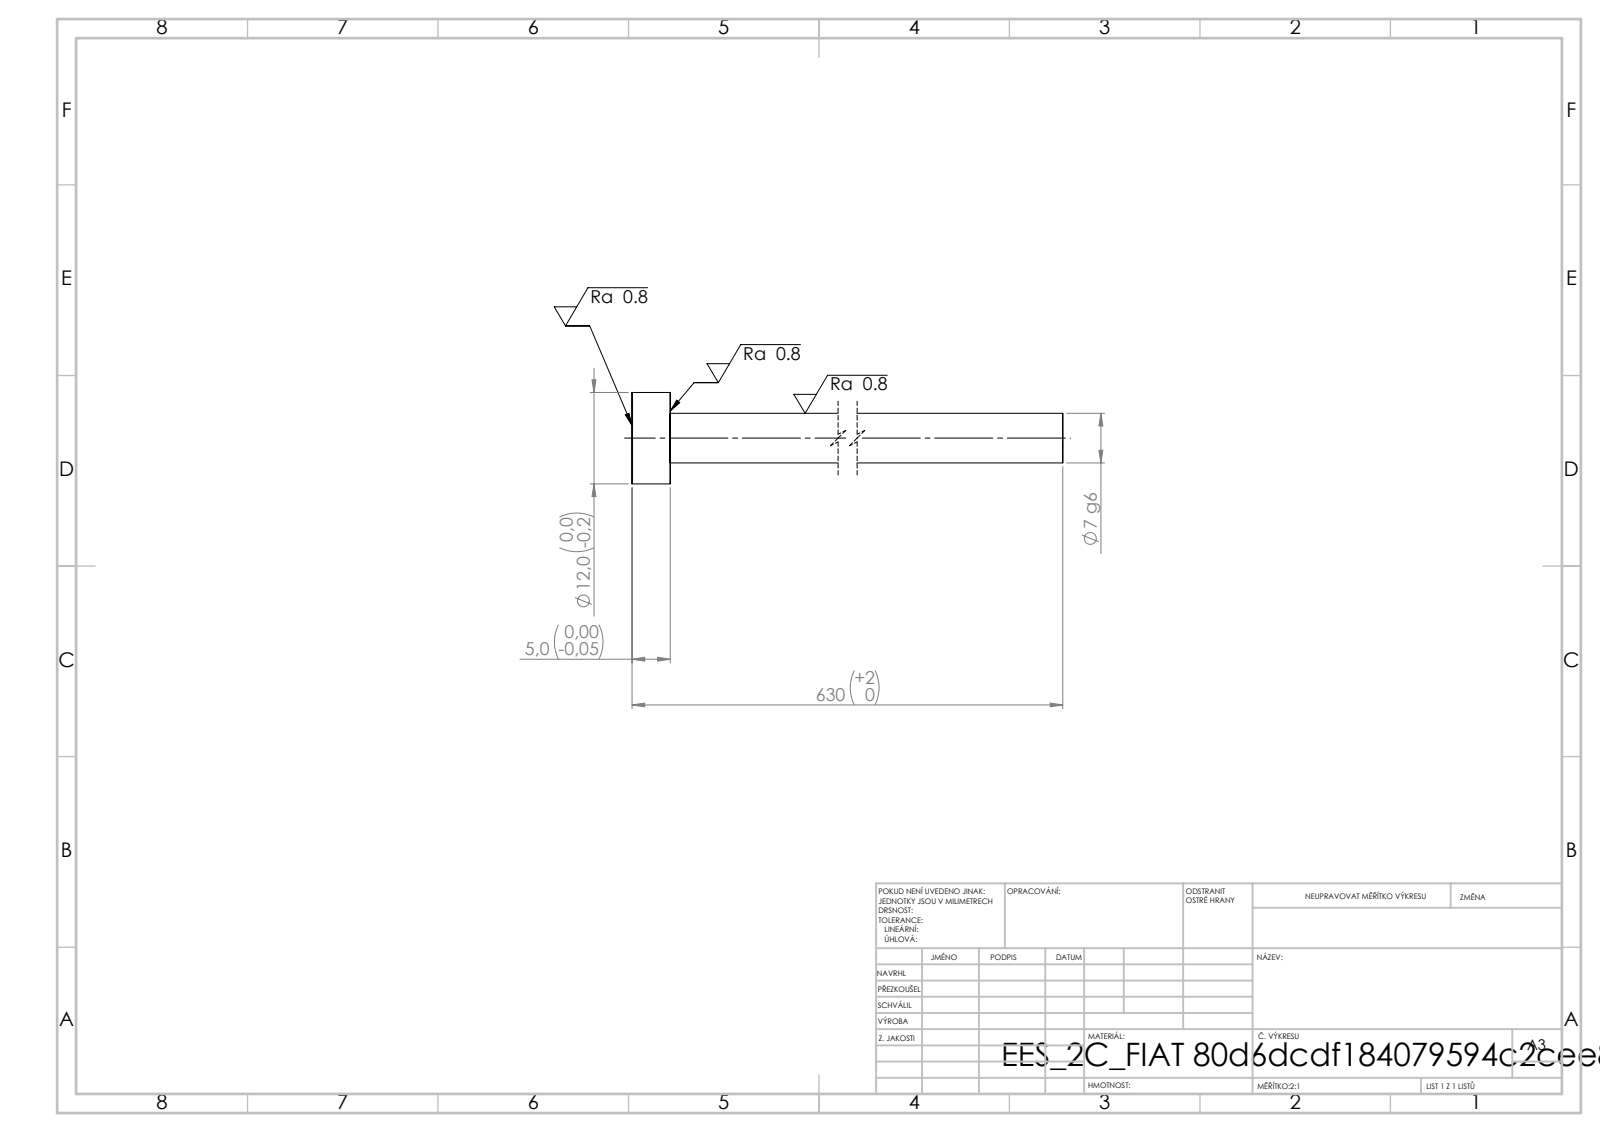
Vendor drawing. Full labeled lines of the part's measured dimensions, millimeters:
STEP written by: SolidWorks 2019 (CONFIG_CONTROL_DESIGN)
Units: millimetres
Bodies: 1 solid, 7 faces (3 planar, 4 cylindrical, 0 other)
Overall size (bounding box): 630 × 12 × 12
Volume: 21 305 mm³ · Surface area: 13 177 mm²
Round bosses / shafts (diameter × count): ⌀12 ×1, ⌀6.5 ×1
Main face-to-face distances: 5, 630, 625
